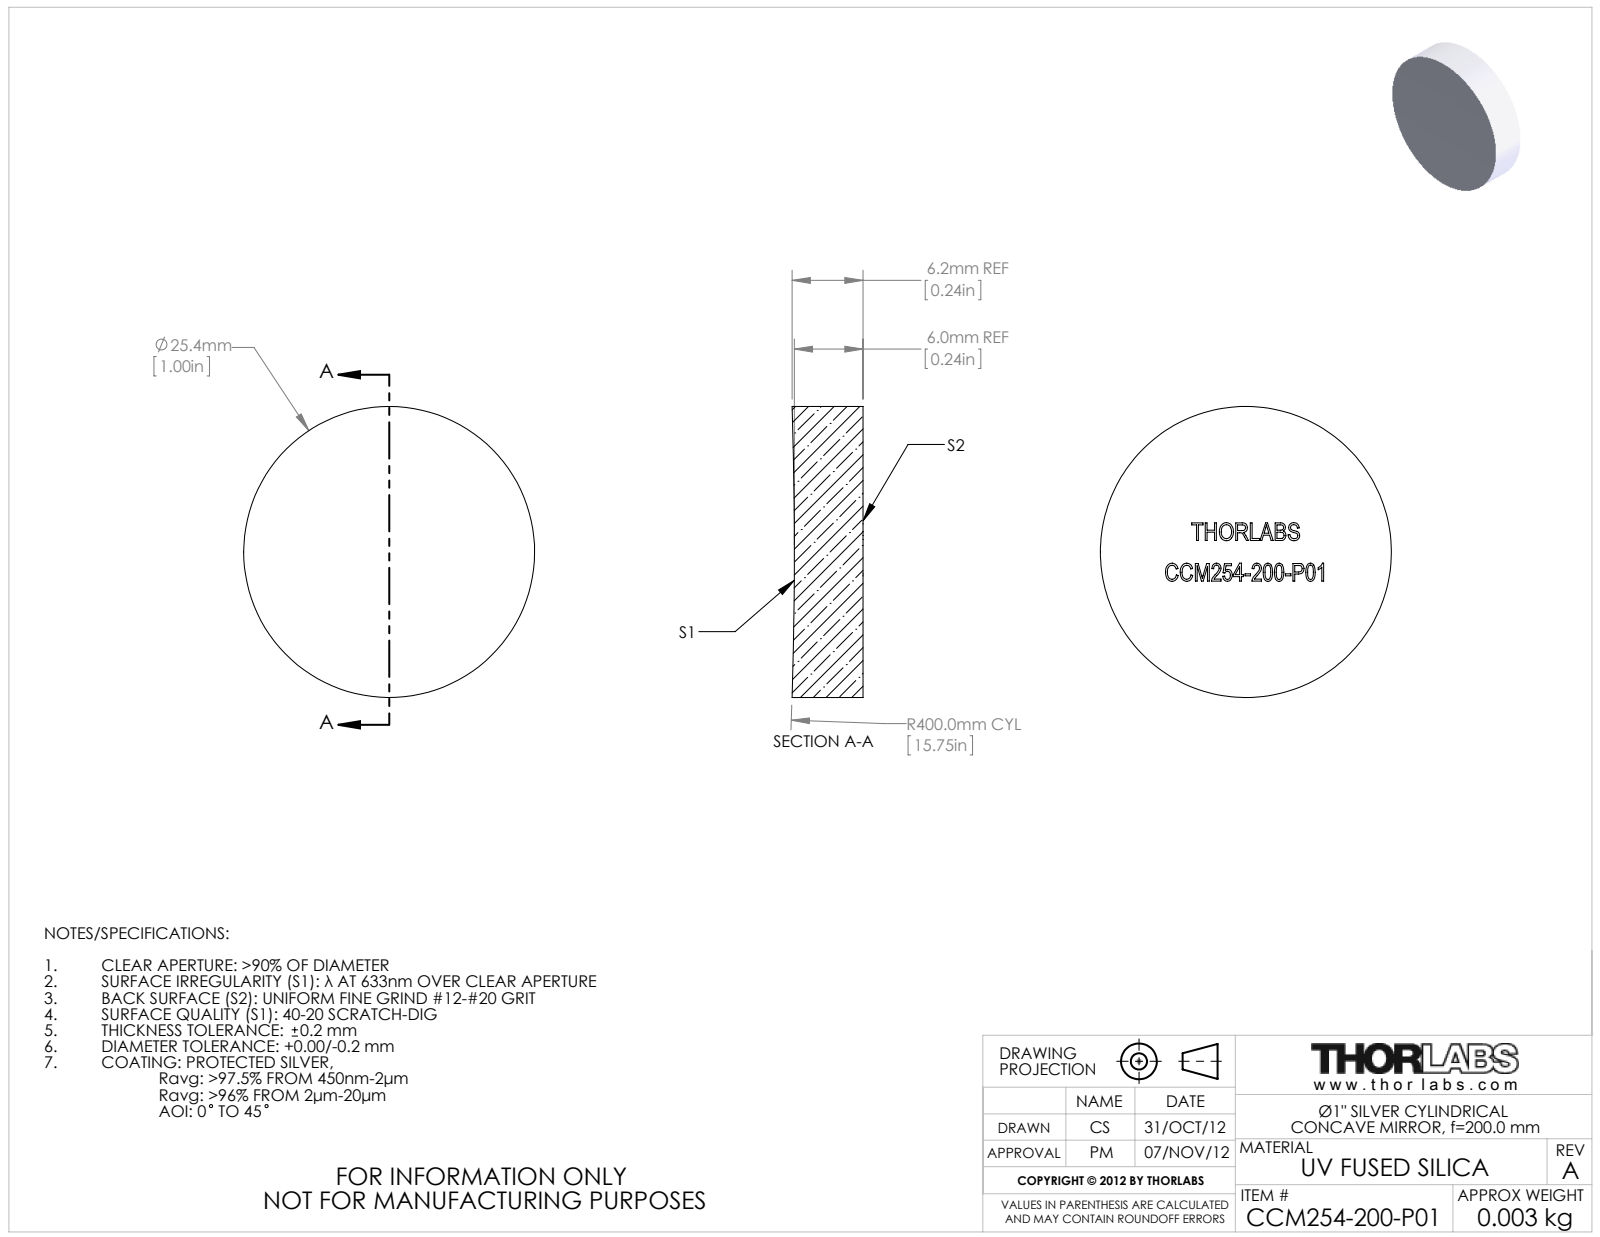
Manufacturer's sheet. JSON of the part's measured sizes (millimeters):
{"part_name": "TTN005971-E0W", "step_written_by": "SolidWorks 2012 (CONFIG_CONTROL_DESIGN)", "units": "millimeters", "bodies": {"solids": 1, "faces": 37, "planar": 33, "cylindrical": 4, "other": 0}, "overall_size": [25.4, 25.4, 6.2], "volume_mm3": 3066, "surface_area_mm2": 1500, "round_bosses_or_shafts": [[25.4, 1]], "partial_cylinders_radius": [[400, 1]]}
